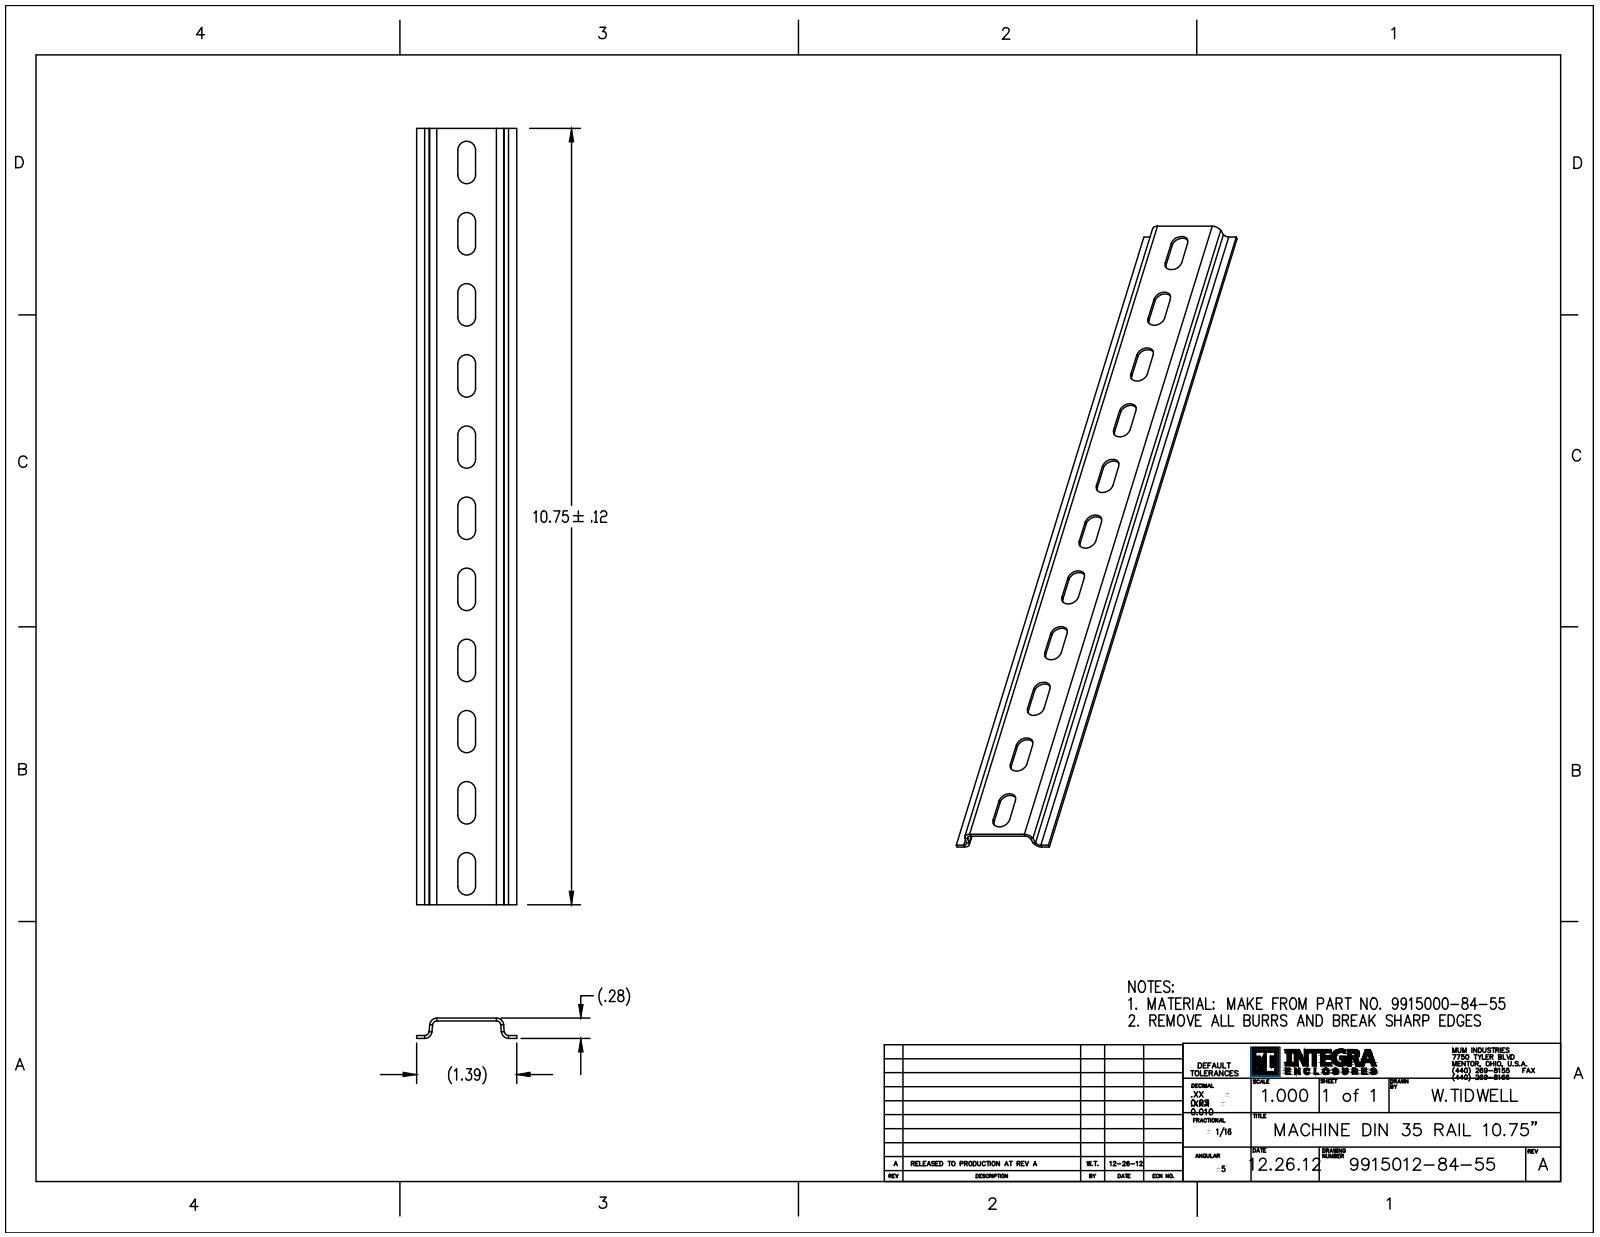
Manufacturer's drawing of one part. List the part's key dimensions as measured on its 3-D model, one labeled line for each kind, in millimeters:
Part name (STEP PRODUCT): DIN12-P10
STEP written by: SolidWorks 2018 (AUTOMOTIVE_DESIGN)
Units: millimetres
Bodies: 1 solid, 66 faces (36 planar, 30 cylindrical, 0 other)
Overall size (bounding box): 273.1 × 35.2 × 7.2
Volume: 11 200 mm³ · Surface area: 23 050 mm²
Partial cylindrical surfaces — rounded edges, fillets, slot ends (radius × count): R3.1 ×14, R3.1 ×8, R1.5 ×4, R2.5 ×4
Main face-to-face distances: 1, 1, 5.1, 6.1, 6.2, 7.2, 35.2, 14.5, 20.7, 6.2
